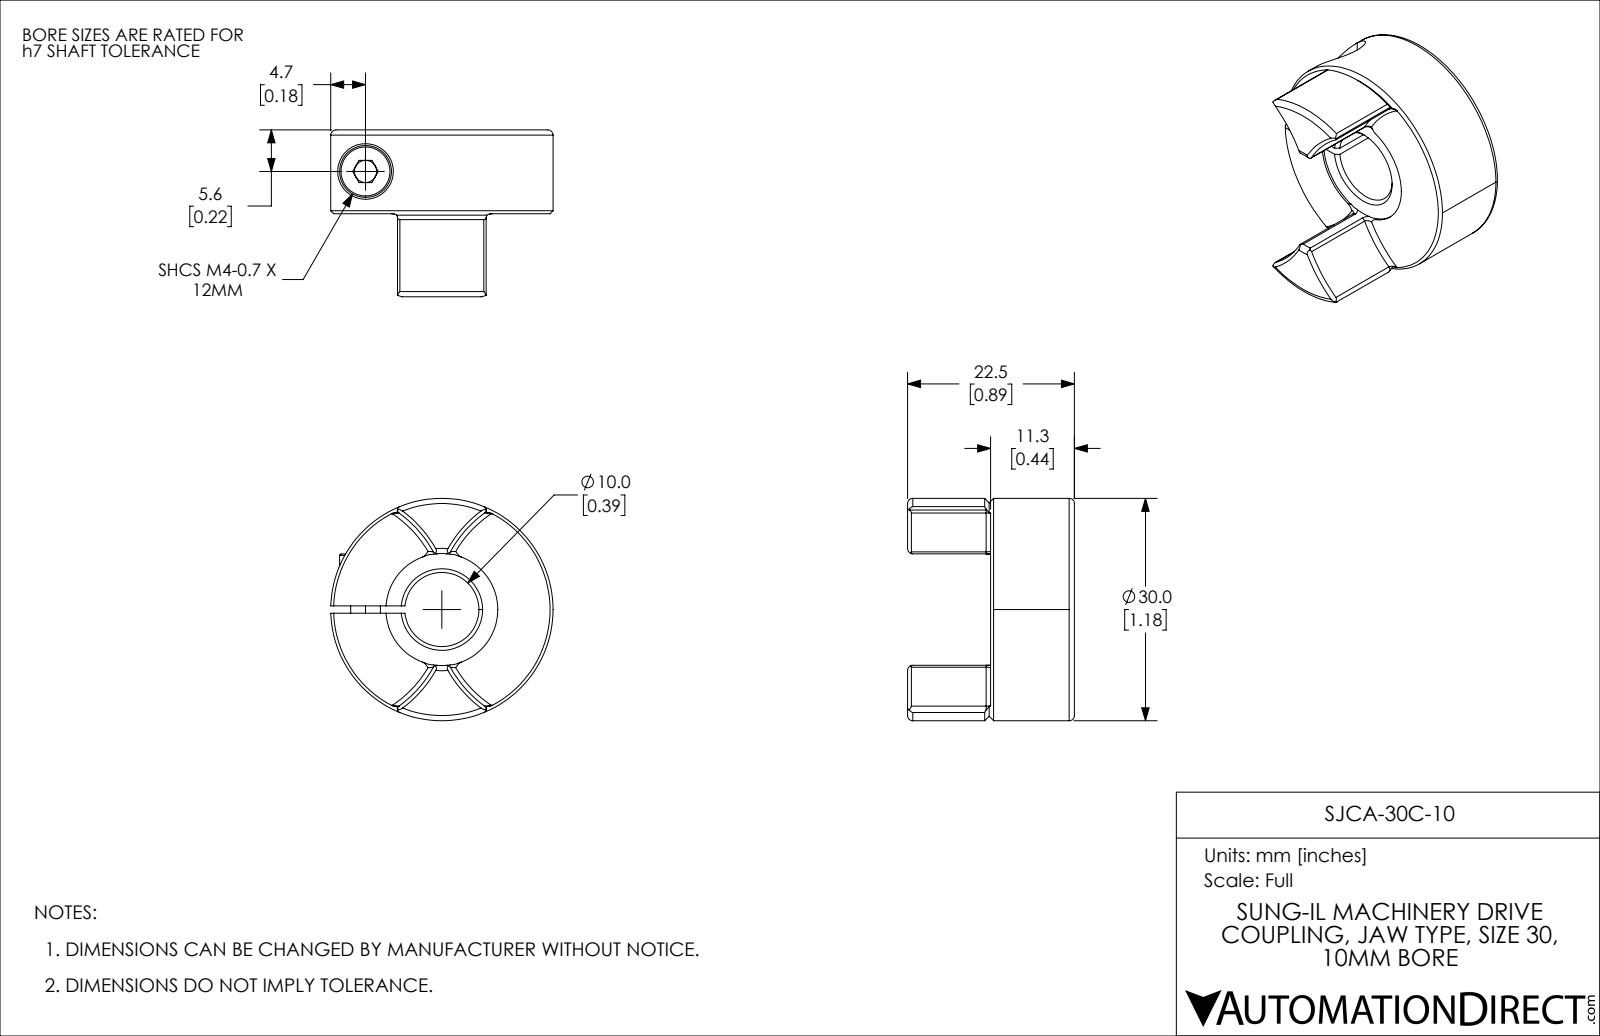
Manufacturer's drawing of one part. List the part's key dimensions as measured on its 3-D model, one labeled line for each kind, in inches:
Part name (STEP PRODUCT): SJCA-30C-10
STEP written by: SolidWorks 2021 (CONFIG_CONTROL_DESIGN)
Units: inches
Bodies: 2 solids, 108 faces (27 planar, 41 cylindrical, 40 other)
Overall size (bounding box): 1.181 × 1.181 × 0.886
Volume: 0.483 in³ · Surface area: 6.36 in²
Round holes (diameter × count): ⌀0.118 ×1, ⌀0.13 ×1, ⌀0.173 ×1, ⌀0.295 ×1, ⌀0.394 ×1, ⌀0.594 ×1
Round bosses / shafts (diameter × count): ⌀1.181 ×1, ⌀0.276 ×1, ⌀0.157 ×1
Partial cylindrical surfaces — rounded edges, fillets, slot ends (radius × count): R0.02 ×8, R0.634 ×2, R1.083 ×1
Main face-to-face distances: 0.445, 0.039, 0.433, 0.157, 0.441, 0.453, 0.886, 0.118, 0.315, 0.276
